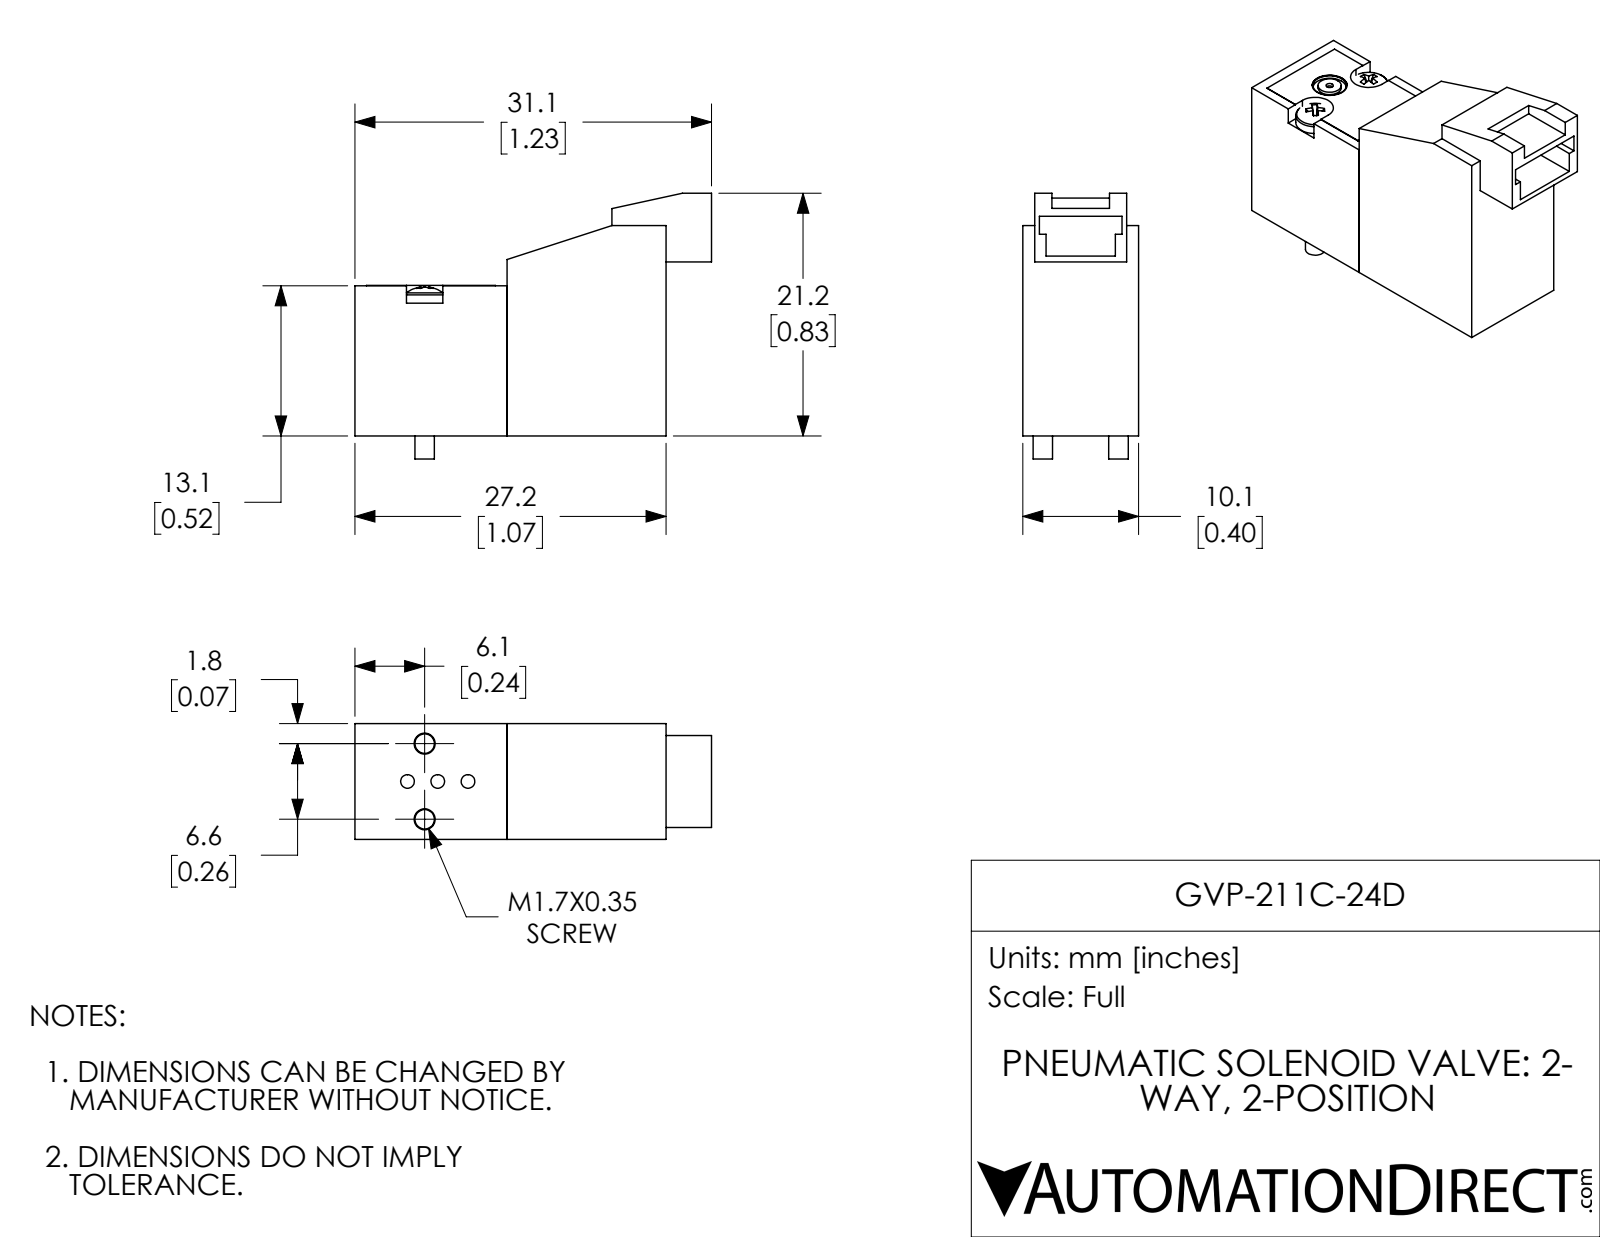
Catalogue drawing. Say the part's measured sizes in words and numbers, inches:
The part is named "GVP-211C-24D". Its 3-D file was written by "SolidWorks 2018 (AUTOMOTIVE_DESIGN)". It is 4 solids with 126 faces: 83 planar, 29 cylindrical and 14 other. Overall it measures 1.226 by 0.913 by 0.398 inches. Its volume is 0.259 cubic inches and its surface area 4.199 square inches. Round holes: 3 of diameter 0.047, 2 of diameter 0.072, 1 of diameter 0.025, 1 of diameter 0.115, 1 of diameter 0.12. Round bosses or shafts: 2 of diameter 0.134, 2 of diameter 0.067, 1 of diameter 0.08. Partial cylindrical surfaces (rounded edges, fillets, slot ends): 2 of radius 0.062. The main face-to-face distances are 0.398, 0.547, 1.07, 0.523, 0.517, 0.238, 0.041, 0.357, 0.755, 0.618. The hole center spacings are 0.104, 0.198, 0.105, 0.137, 0.138, 0.143, 0.143, 0.143.
